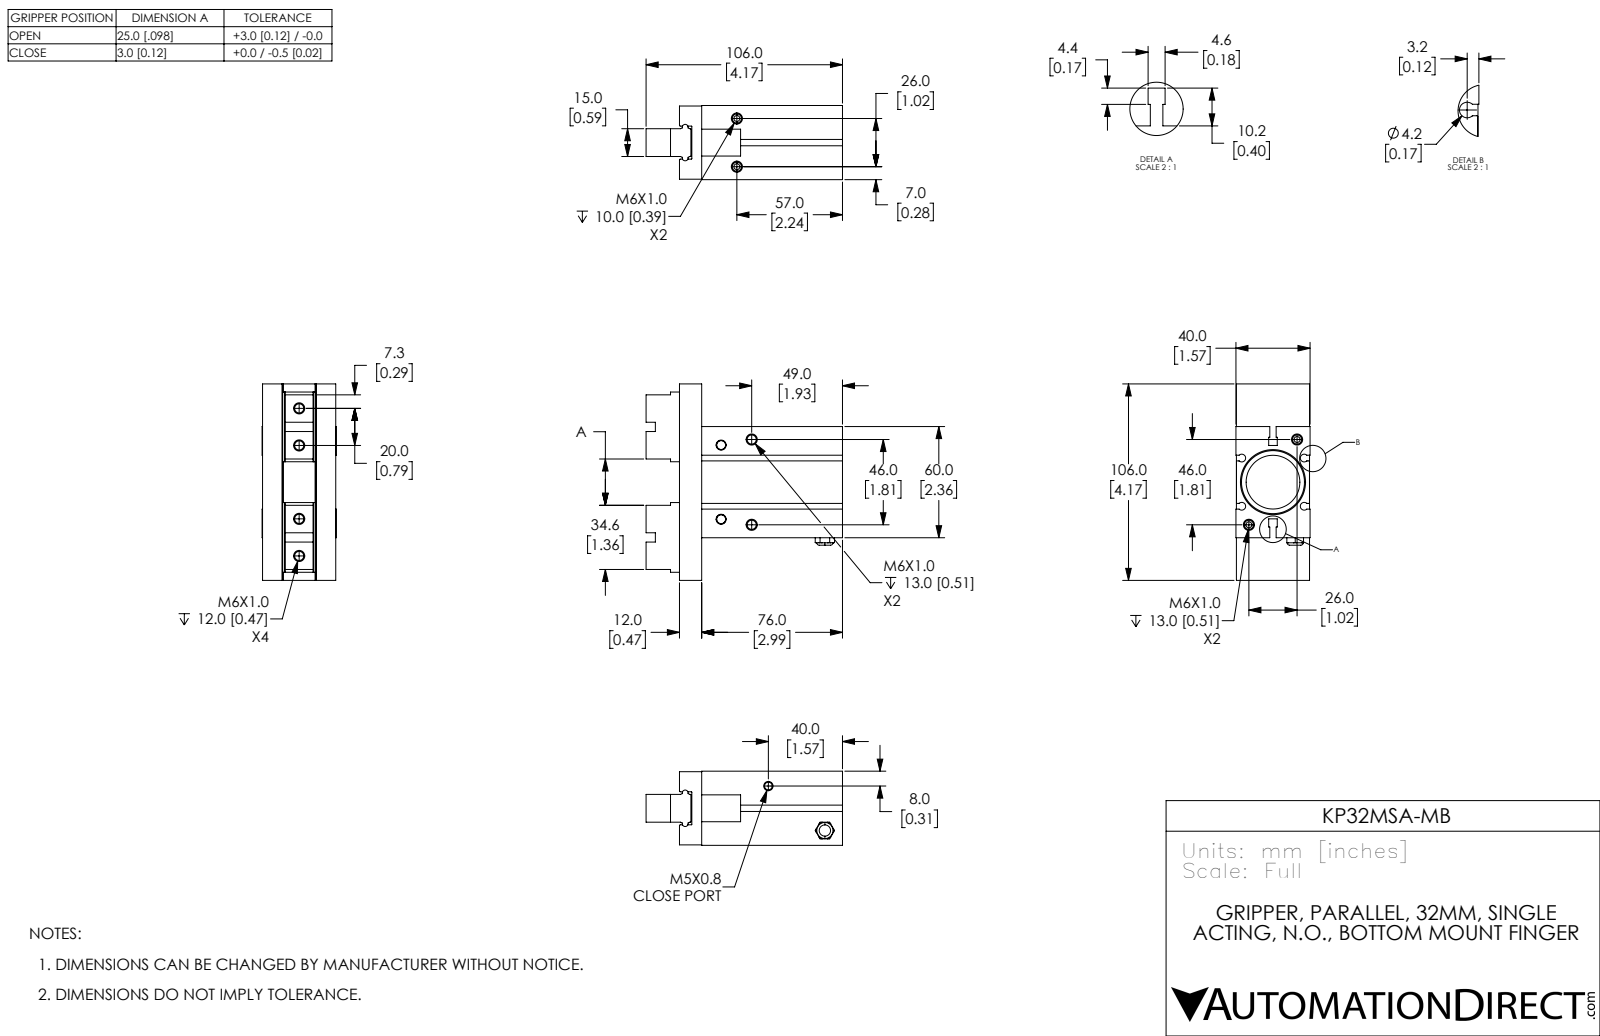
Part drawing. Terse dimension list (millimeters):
name: KP32MSA-MB-2; KP32MSA-MB-1; KP32MSA-MB-3; KP32MSA-MB
written by: SolidWorks 2017 (CONFIG_CONTROL_DESIGN)
unit: mm
bodies: 3 solids, 261 faces (135 planar, 64 cylindrical, 62 other)
size: 106 × 106 × 40
volume: 209 878 mm³; area: 48 358 mm²
holes: 6× ⌀4.92, 4× ⌀4.92, 2× ⌀0.5, 2× ⌀4.13, 2× ⌀6.02, 1× ⌀6.1, 1× ⌀29, 1× ⌀34
rounds: 6× R0.2, 4× R2.1, 2× R0.3, 2× R1.59
face distances: 12.5, 27.25, 39.7, 27.5, 12.2, 27.2, 12.75, 39.75, 12.25, 39.45
hole spacings: 13.39, 19.8, 20, 21.24, 26.42, 39.8, 44.73, 59.6
